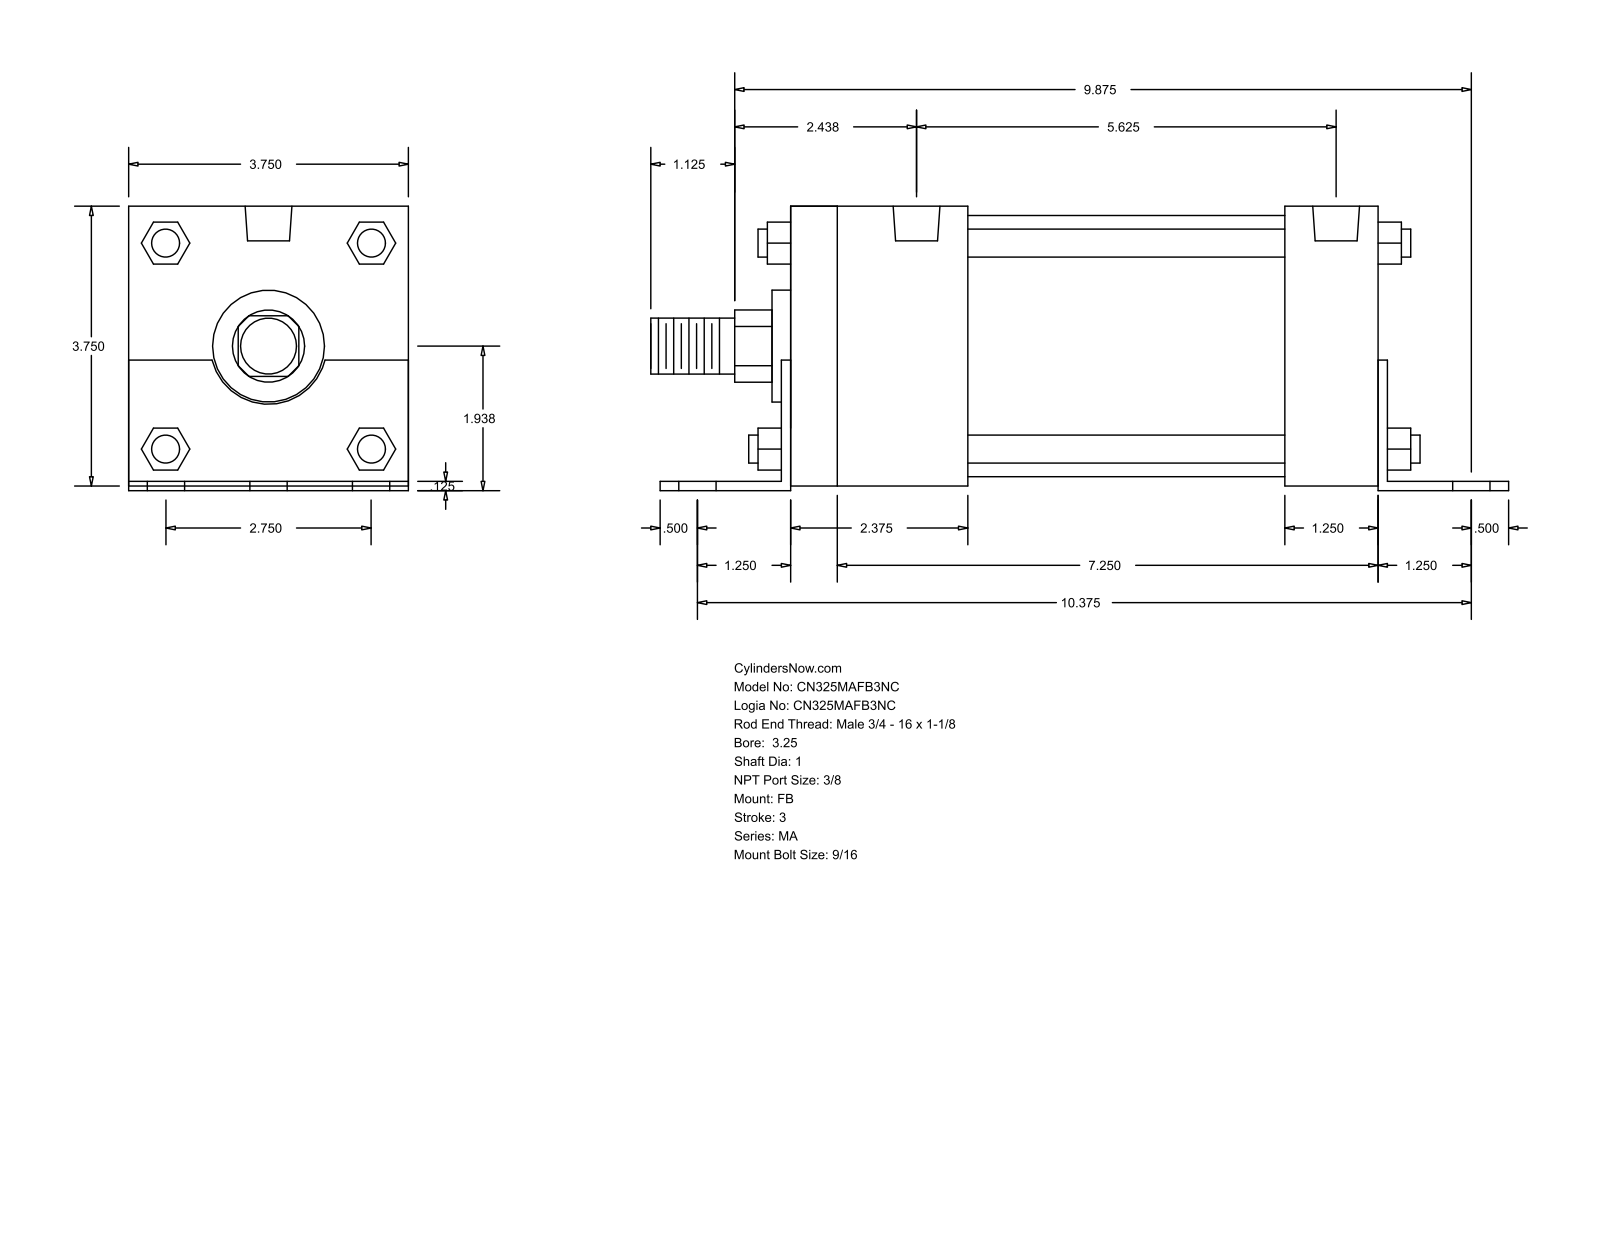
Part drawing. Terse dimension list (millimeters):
name: MA_FB__0325_1
written by: GSSL Pune (CONFIG_CONTROL_DESIGN)
unit: mm
bodies: 0 solids, 140 faces (105 planar, 35 cylindrical, 0 other)
size: 292.1 × 96.84 × 95.25
holes: 6× ⌀14.29, 4× ⌀11.11, 2× ⌀15.93
bosses: 4× ⌀9.53, 1× ⌀88.9, 1× ⌀38.1, 1× ⌀25.4, 1× ⌀19.05
rounds: 1× R12.29, 1× R19.81
face distances: 95.24, 3.17, 1.59, 96.83, 1.58, 93.66, 3.18, 200.02, 206.37, 203.2
hole spacings: 34.92, 265.82, 263.52, 4.76, 57.78, 61.64, 69.84, 82.38
